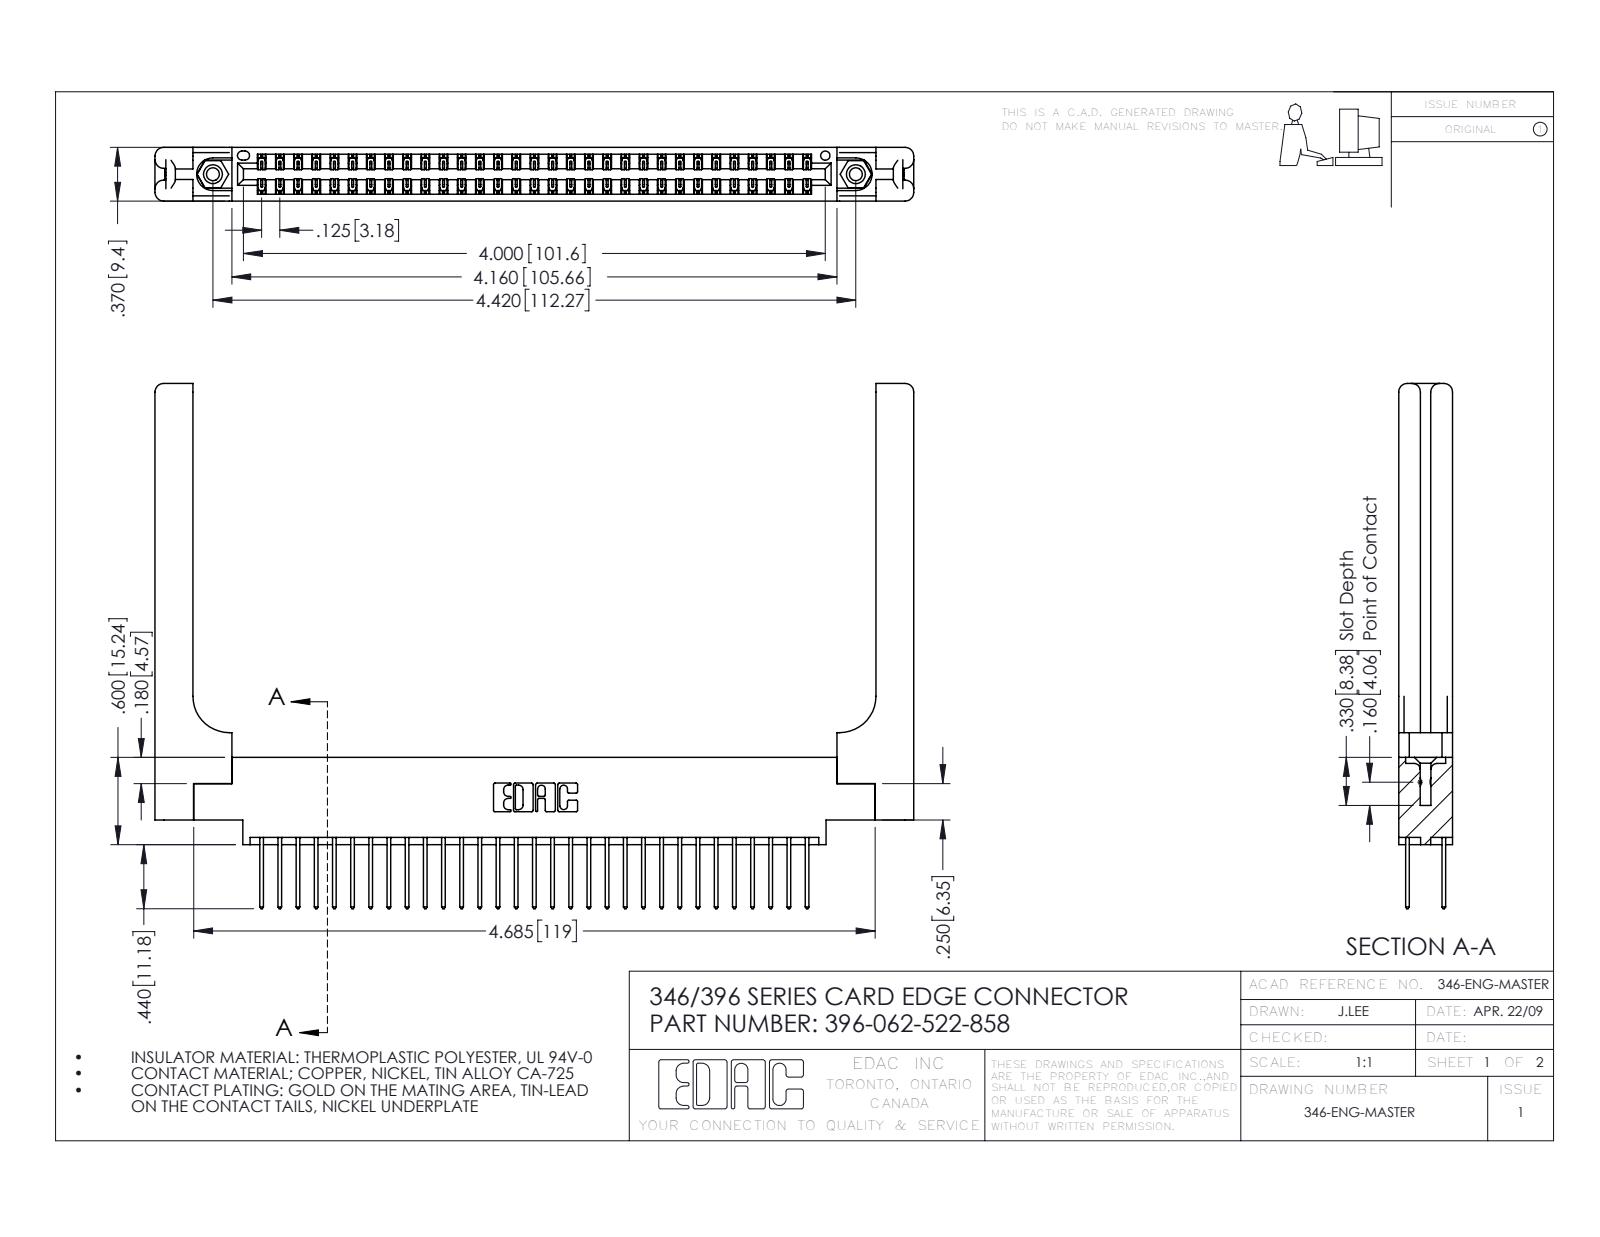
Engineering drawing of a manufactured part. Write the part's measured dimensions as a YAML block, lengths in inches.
part_name: "396-062-522-858; 346-220-058_345-220-058; 345-250-001_345-250-001-102; 345-292-001_345-293-122 (+1 more)"
step_written_by: "SolidWorks 2016 (CONFIG_CONTROL_DESIGN)"
units: inches
bodies: {solids: 67, faces: 3606, planar: 2398, cylindrical: 1148, other: 60}
overall_size: [5.216, 3.61, 0.37]
volume: 1.241
surface_area: 36.21
round_holes:
  - {diameter: 0.089, count: 2}
  - {diameter: 0.125, count: 2}
  - {diameter: 0.156, count: 2}
  - {diameter: 0.064, count: 1}
round_bosses_or_shafts:
  - {diameter: 0.155, count: 2}
partial_cylinders:
  - {radius: 0.006, count: 93}
  - {radius: 0.01, count: 62}
  - {radius: 0.01, count: 22}
  - {radius: 0.06, count: 16}
  - {radius: 0.007, count: 6}
  - {radius: 0.031, count: 6}
  - {radius: 0.026, count: 3}
  - {radius: 0.014, count: 2}
face_to_face_distances: [0.37, 0.048, 0.322, 0.072, 0.25, 0.148, 0.15, 0.025, 0.298, 0.275]
hole_center_spacings: [0.246, 4.212, 4.42]
